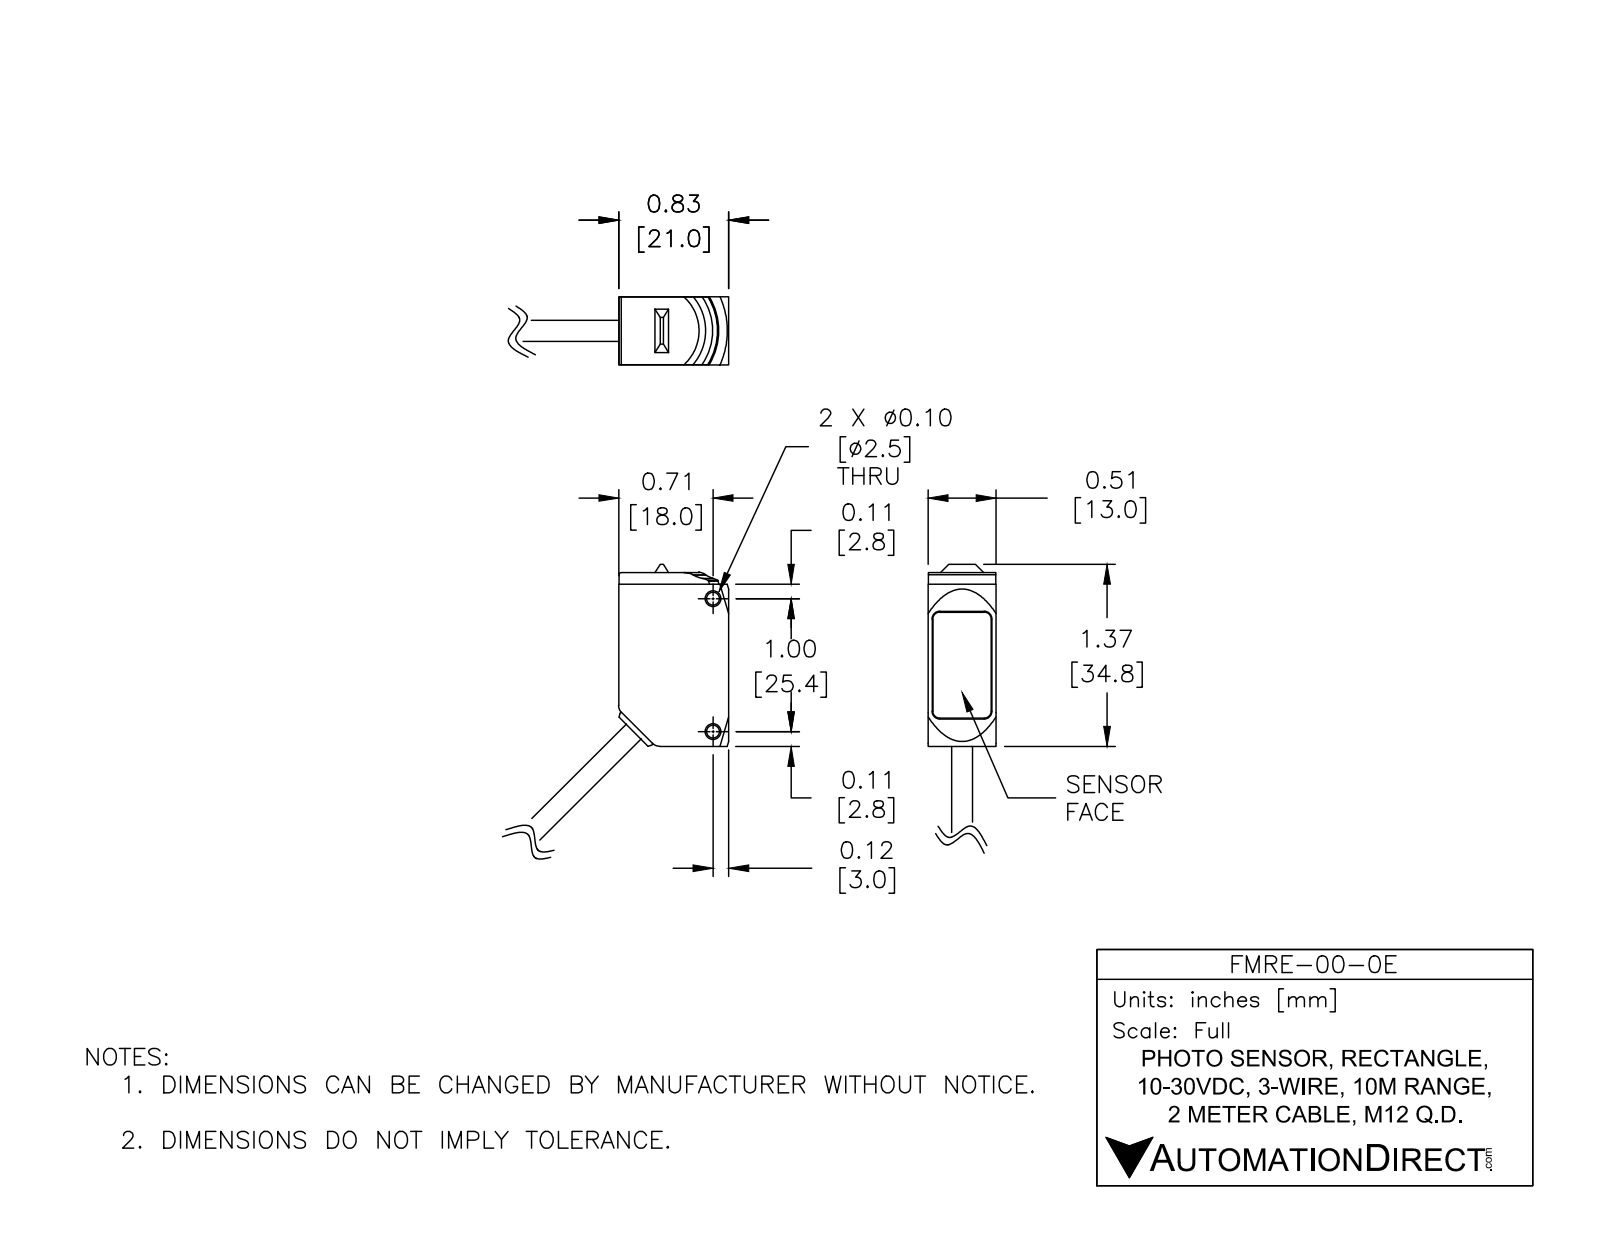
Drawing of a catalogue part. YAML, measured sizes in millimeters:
part_name: "FMRE-00-0E"
step_written_by: "SolidWorks 2017 (AUTOMOTIVE_DESIGN)"
units: millimeters
bodies: {solids: 1, faces: 104, planar: 44, cylindrical: 39, other: 21}
overall_size: [52.9, 39.1, 13]
volume: 8870
surface_area: 3443
round_holes:
  - {diameter: 2.5, count: 2}
round_bosses_or_shafts:
  - {diameter: 4, count: 1}
partial_cylinders:
  - {radius: 0.5, count: 7}
  - {radius: 0.5, count: 7}
  - {radius: 1.3, count: 4}
  - {radius: 1.5, count: 4}
  - {radius: 2, count: 2}
  - {radius: 2.4, count: 2}
  - {radius: 2.4, count: 2}
  - {radius: 16.5, count: 2}
face_to_face_distances: [13, 21, 33.2, 0.9, 13, 0.9, 12, 12, 0.8, 12.2]
hole_center_spacings: [25.4]
